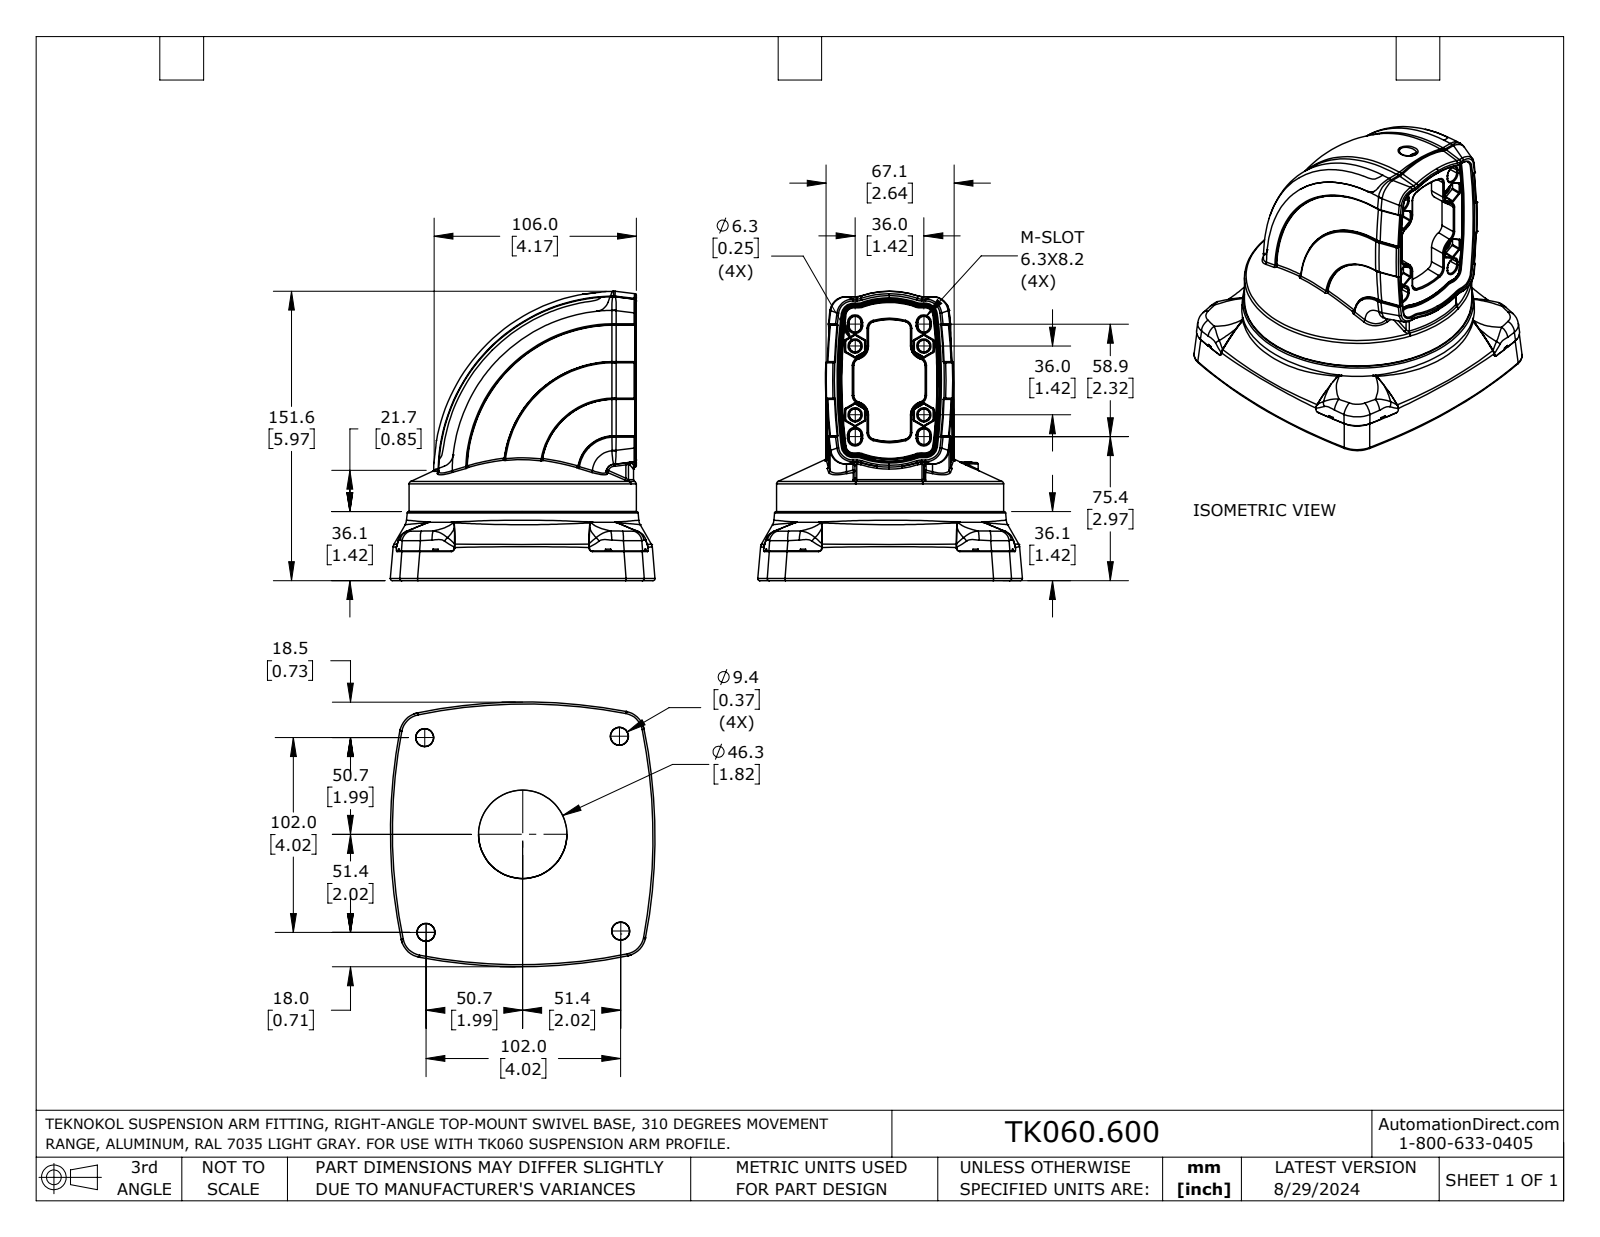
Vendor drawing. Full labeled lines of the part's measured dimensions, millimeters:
Part name (STEP PRODUCT): TK060.600
STEP written by: SolidWorks 2023 (AUTOMOTIVE_DESIGN)
Units: millimetres
Bodies: 1 solid, 1150 faces (218 planar, 214 cylindrical, 718 other)
Overall size (bounding box): 151.6 × 138.7 × 138.7
Volume: 1 203 000 mm³ · Surface area: 96 390 mm²
Round holes (diameter × count): ⌀3.6 ×8, ⌀4 ×1, ⌀46.3 ×1
Round bosses / shafts (diameter × count): ⌀3.6 ×8, ⌀119 ×1
Partial cylindrical surfaces — rounded edges, fillets, slot ends (radius × count): R0.5 ×61, R0.6 ×32, R0.4 ×20, R0.2 ×12, R2.4 ×12, R1.4 ×10, R1.4 ×8, R1 ×4
Main face-to-face distances: 10.2, 15.6, 5.4, 1.8, 8.7, 13.8, 3.6, 13.8, 3.7, 1.8
Hole centre spacings: 98.5, 23.4, 69.6, 69.6, 113.6, 137.3, 43.3, 80.5
